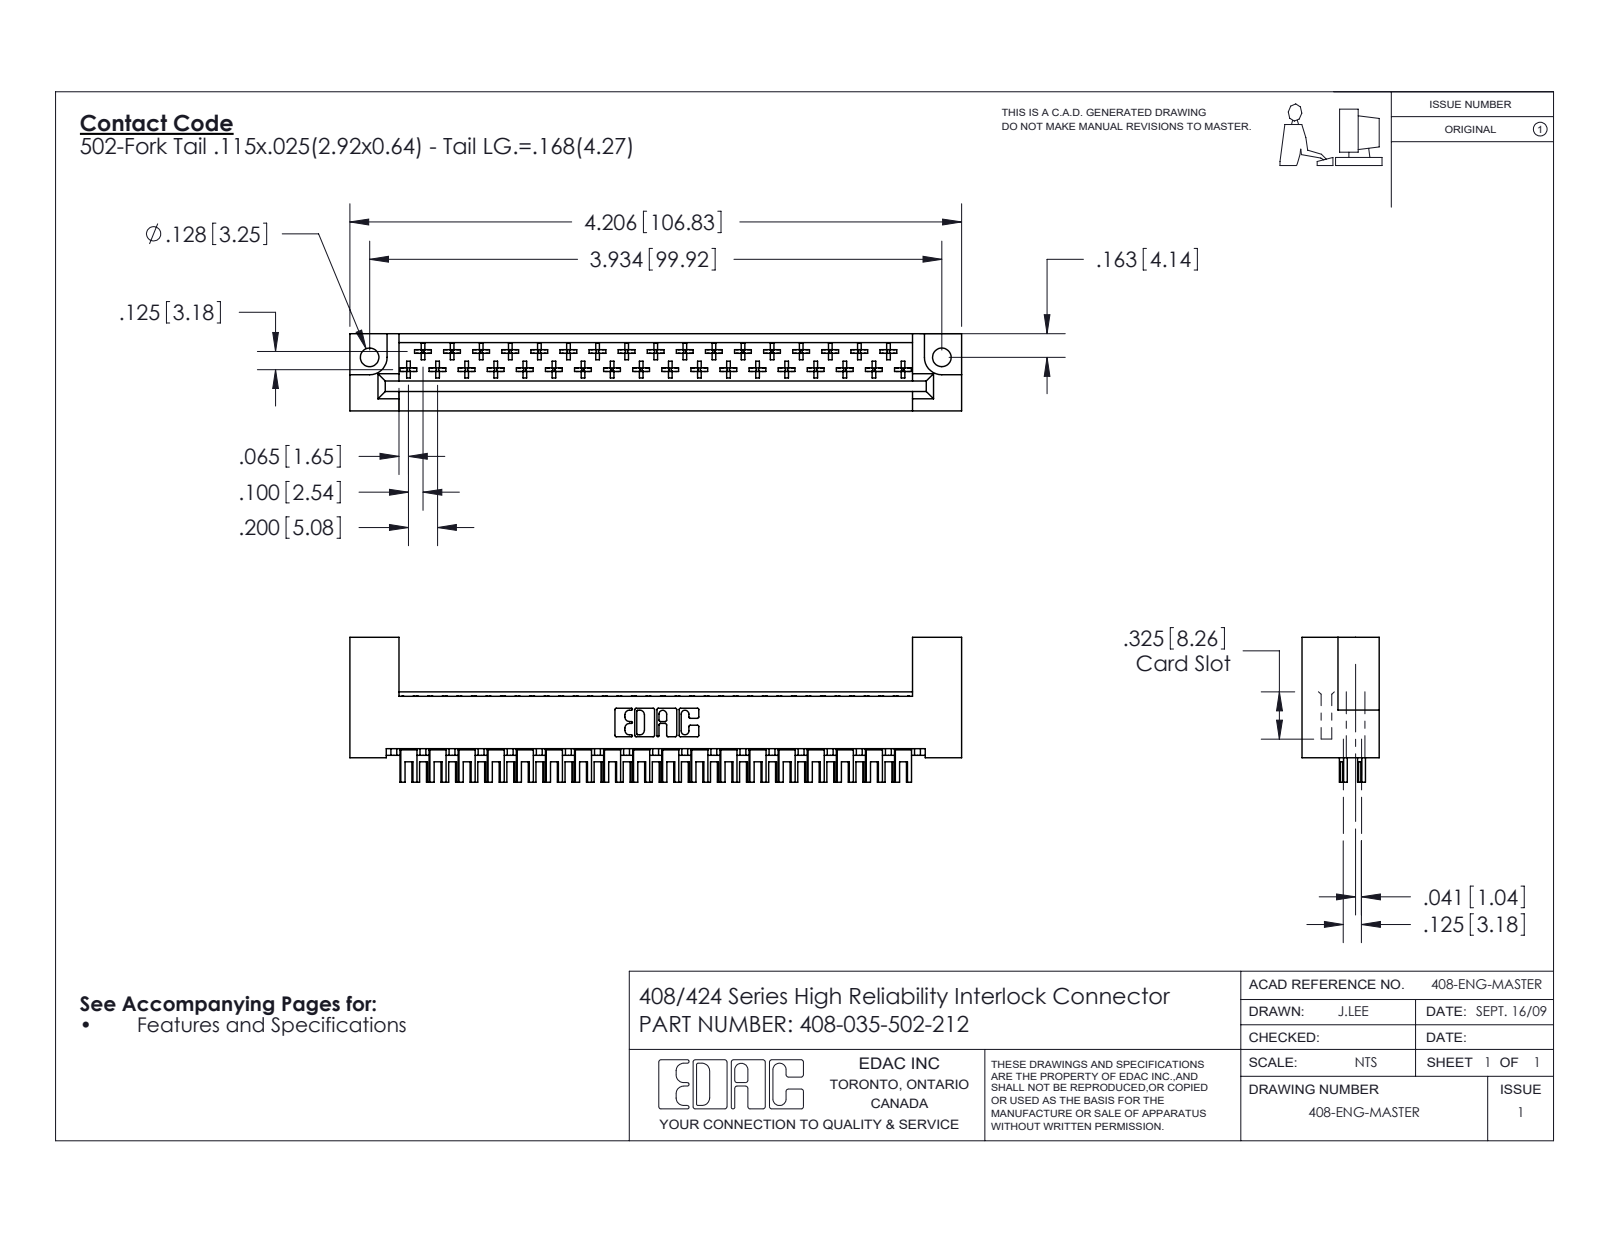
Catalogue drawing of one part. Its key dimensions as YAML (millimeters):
part_name: "408-290-001_408-290-102; 408 Part_035 - 2; 408-035-502-212"
step_written_by: "SolidWorks 2016 (CONFIG_CONTROL_DESIGN)"
units: millimeters
bodies: {solids: 36, faces: 1994, planar: 1524, cylindrical: 330, other: 140}
overall_size: [106.8, 25.3, 13.5]
volume: 13400
surface_area: 15750
round_holes:
  - {diameter: 3.3, count: 2}
partial_cylinders:
  - {radius: 0.3, count: 210}
  - {radius: 0.5, count: 37}
  - {radius: 0.3, count: 22}
  - {radius: 0.2, count: 6}
  - {radius: 0.8, count: 6}
  - {radius: 0.7, count: 3}
  - {radius: 3, count: 2}
face_to_face_distances: [13.5, 3.2, 2.5, 0.6, 0.6, 9.2, 6, 6.6, 5.5, 6.9]
hole_center_spacings: [99.9]
